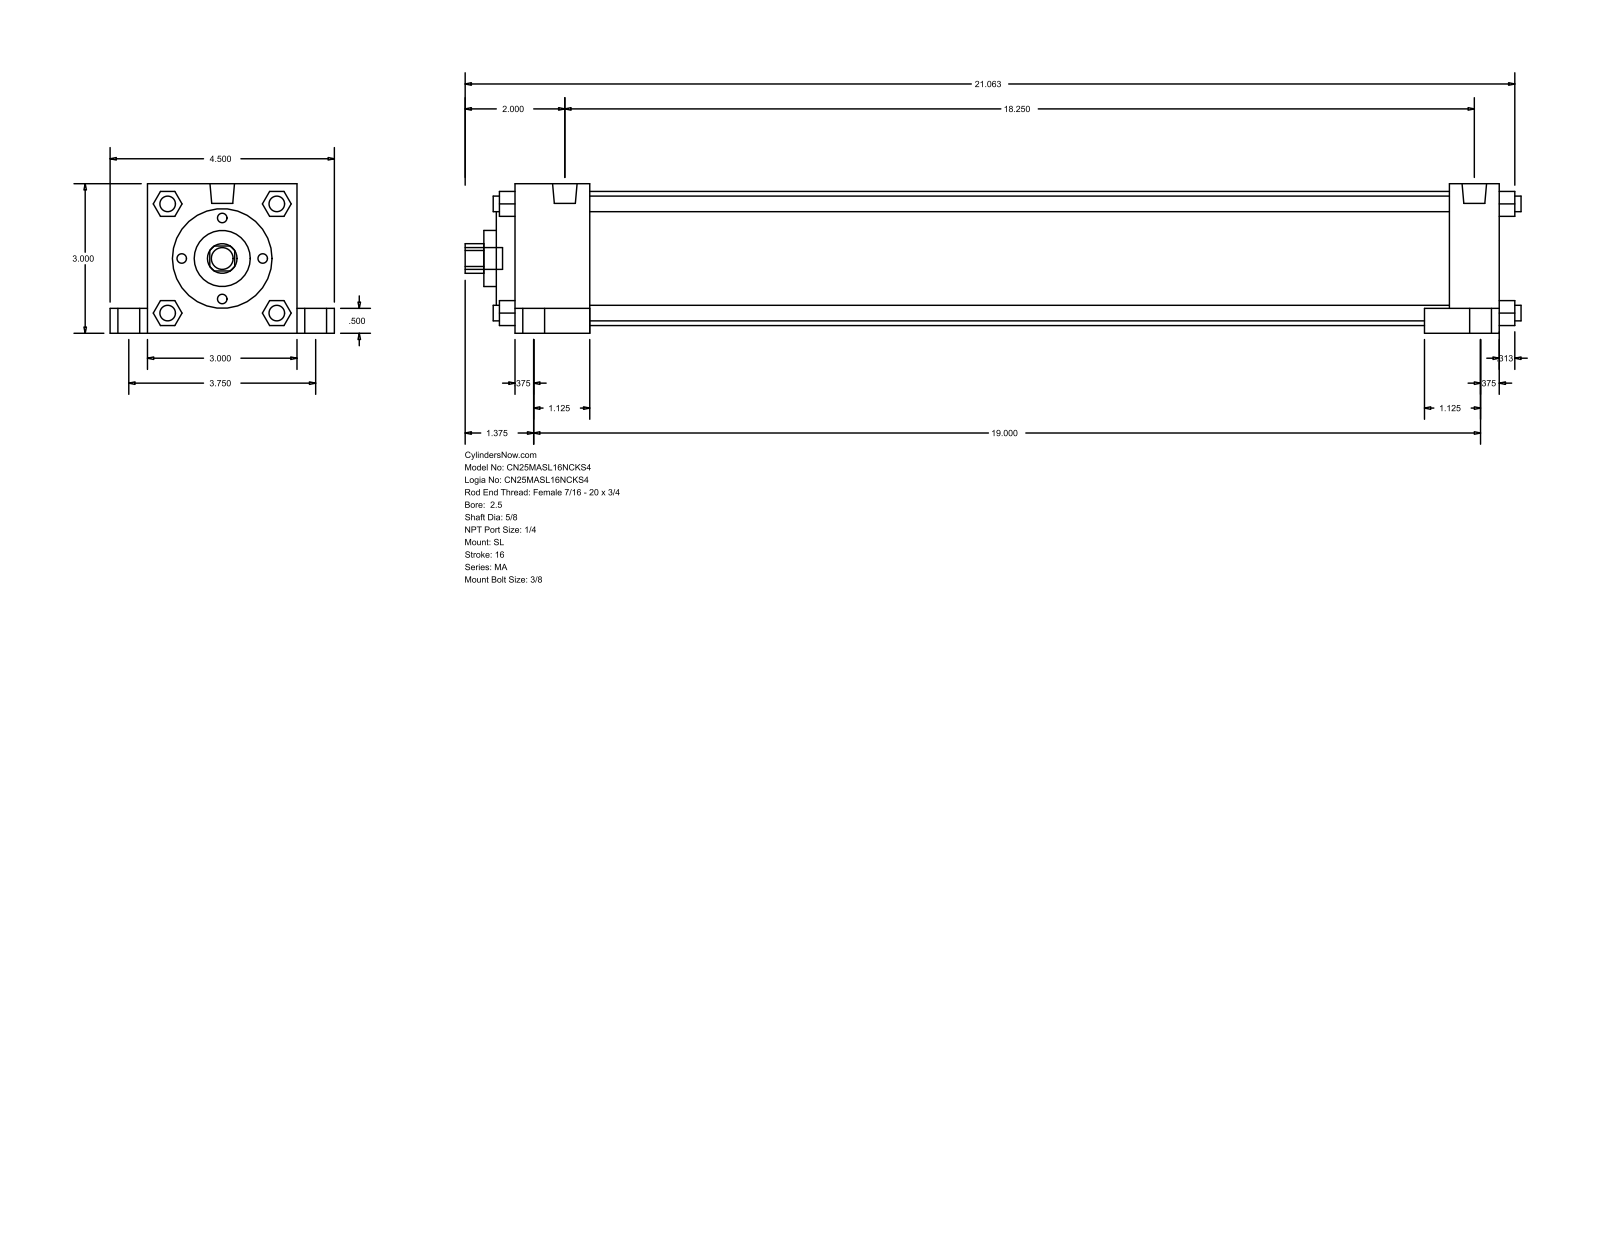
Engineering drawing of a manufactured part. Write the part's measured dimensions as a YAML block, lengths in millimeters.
part_name: "MA_SL__0250_0.625"
step_written_by: "GSSL Pune (CONFIG_CONTROL_DESIGN)"
units: millimeters
bodies: {solids: 0, faces: 150, planar: 113, cylindrical: 37, other: 0}
overall_size: [538.16, 114.3, 76.2]
round_holes:
  - {diameter: 15.88, count: 1}
  - {diameter: 28.57, count: 1}
  - {diameter: 50.8, count: 1}
  - {diameter: 68.33, count: 1}
round_bosses_or_shafts:
  - {diameter: 7.94, count: 8}
  - {diameter: 11.11, count: 5}
  - {diameter: 17.46, count: 4}
  - {diameter: 12.49, count: 2}
partial_cylinders:
  - {radius: 7.54, count: 1}
face_to_face_distances: [76.2, 501.65, 12.7, 438.15, 25.4, 38.1, 463.55, 476.25, 19.05, 63.5]
